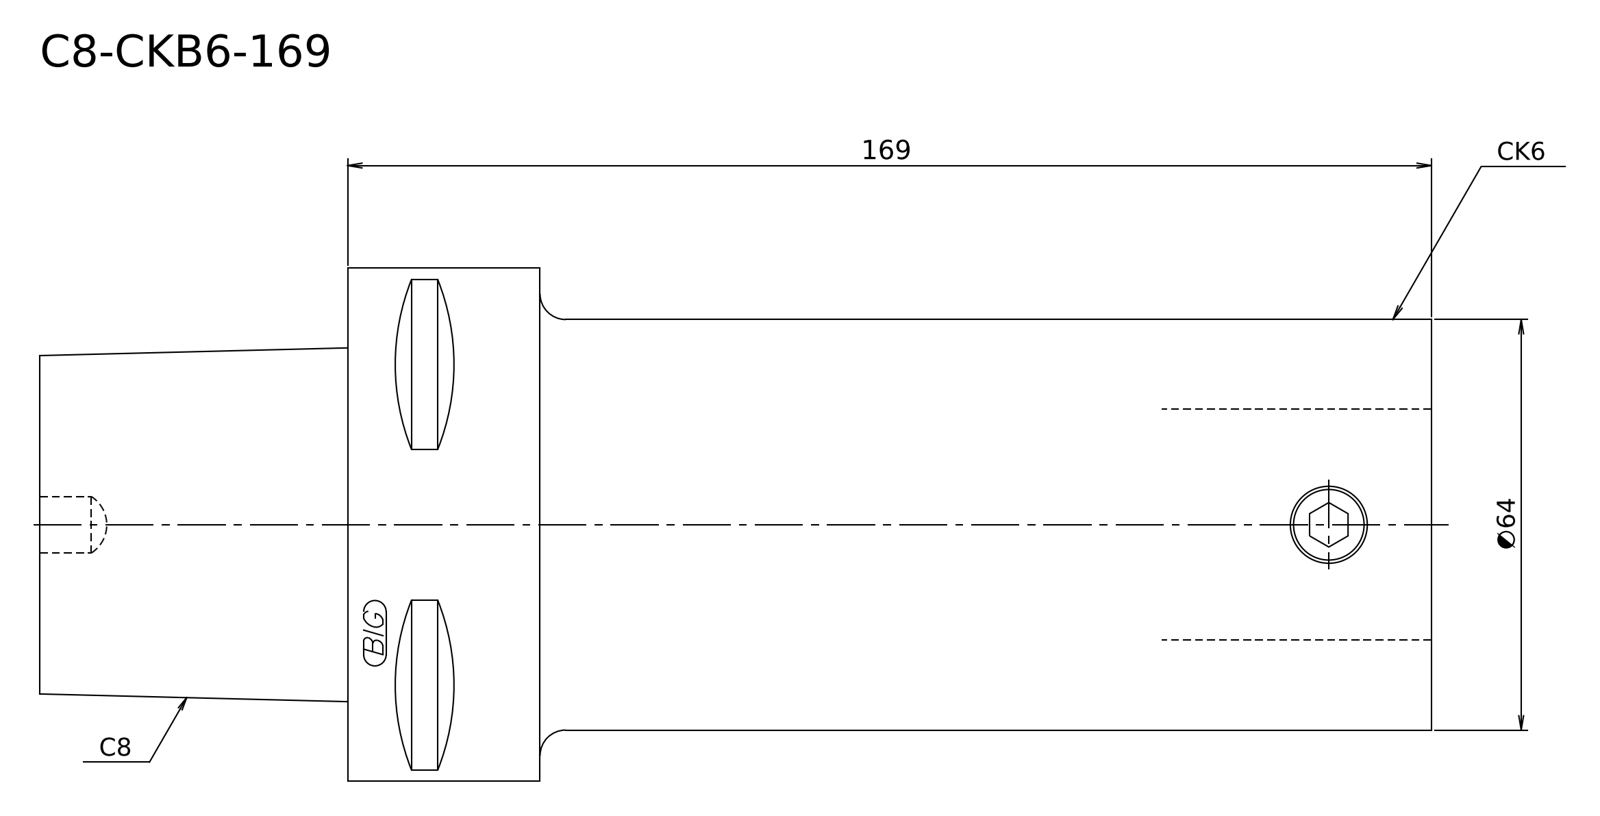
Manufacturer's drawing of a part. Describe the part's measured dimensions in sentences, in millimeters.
Its 3-D file was written by "Kubotek KeyCreator V8.5.1 (14335) (CONFIG_CONTROL_DESIGN)". It is 1 solid with 8 faces: 4 planar, 2 cylindrical and 2 other. Overall it measures 217 by 79.98 by 79.98 millimeters. Its volume is 705 894 cubic millimeters and its surface area 53 019 square millimeters. Round bosses or shafts: 1 of diameter 79.98, 1 of diameter 64. The main face-to-face distances are 169, 217, 48, 139, 30, 78.
